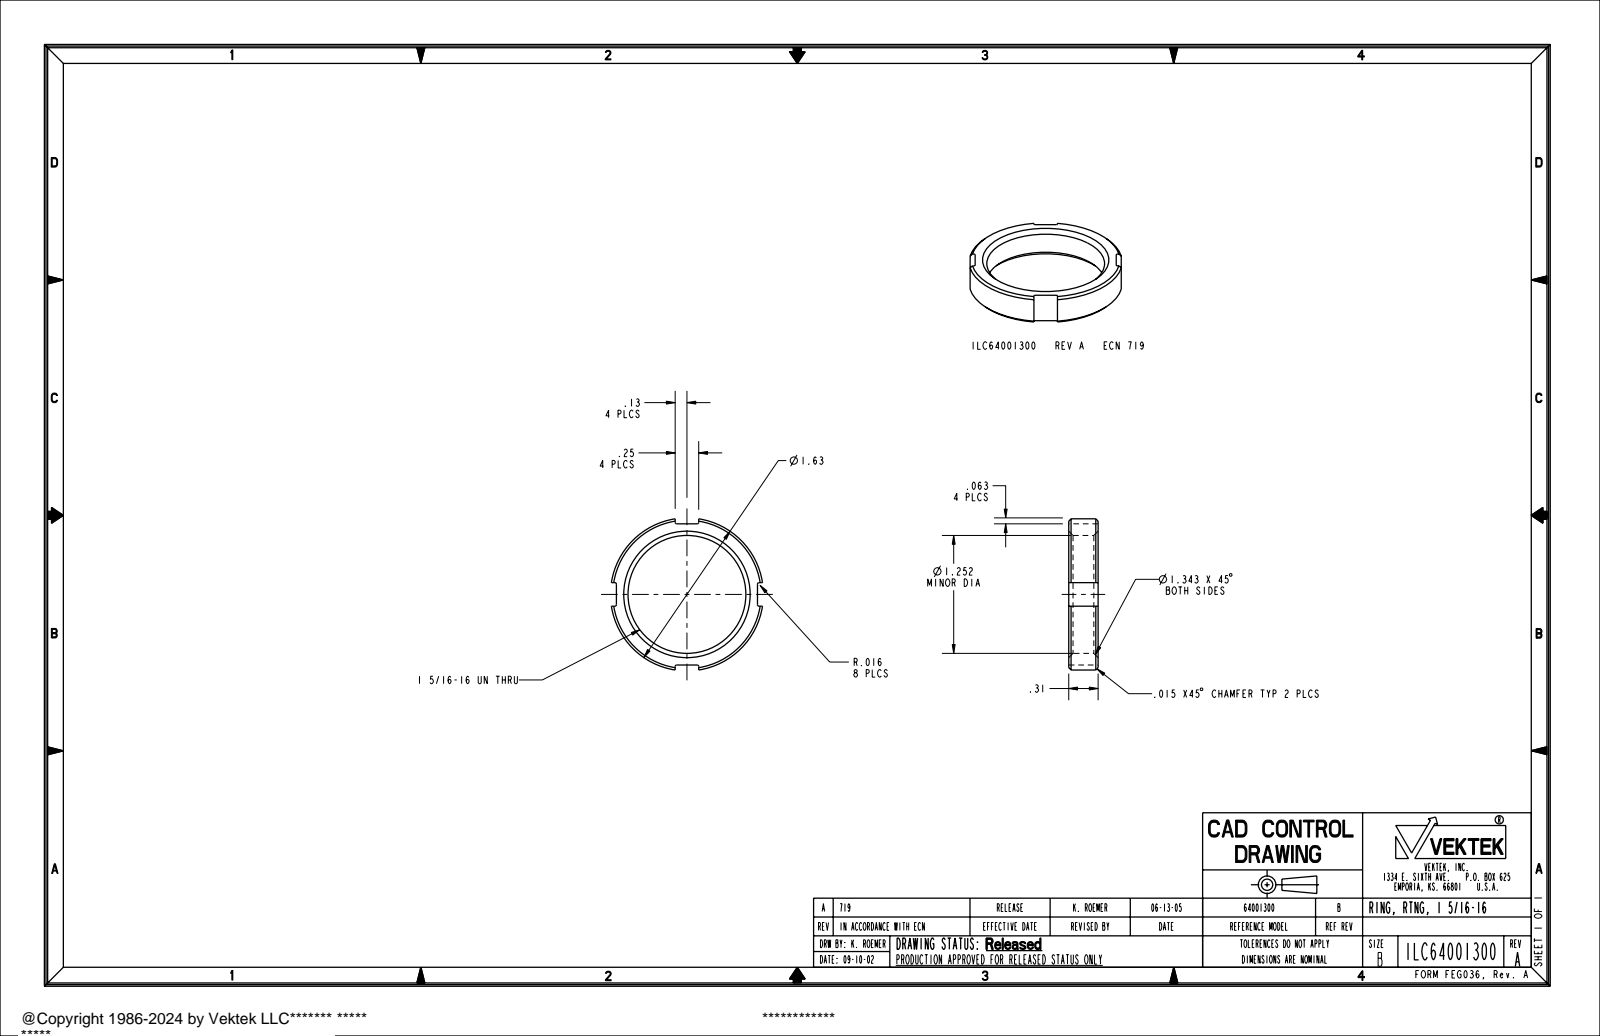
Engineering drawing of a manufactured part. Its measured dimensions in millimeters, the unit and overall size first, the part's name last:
Units: millimetres
Overall size (bounding box): 41.3 × 41.3 × 7.9
Round holes (diameter × count): ⌀31.8 ×1
Round bosses / shafts (diameter × count): ⌀41.3 ×1
Partial cylindrical surfaces — rounded edges, fillets, slot ends (radius × count): R0.4 ×8
Main face-to-face distances: 7.9, 38, 15.8, 22.2, 6.4
Volume: 3 830 mm³ · Surface area: 2 692 mm²
Bodies: 1 solid, 40 faces (14 planar, 14 cylindrical, 12 other)
Part name (STEP PRODUCT): ILC64001300
STEP written by: PRO/ENGINEER BY PARAMETRIC TECHNOLOGY CORPORATION, 2004290 (AUTOMOTIVE_DESIGN_CC2)
